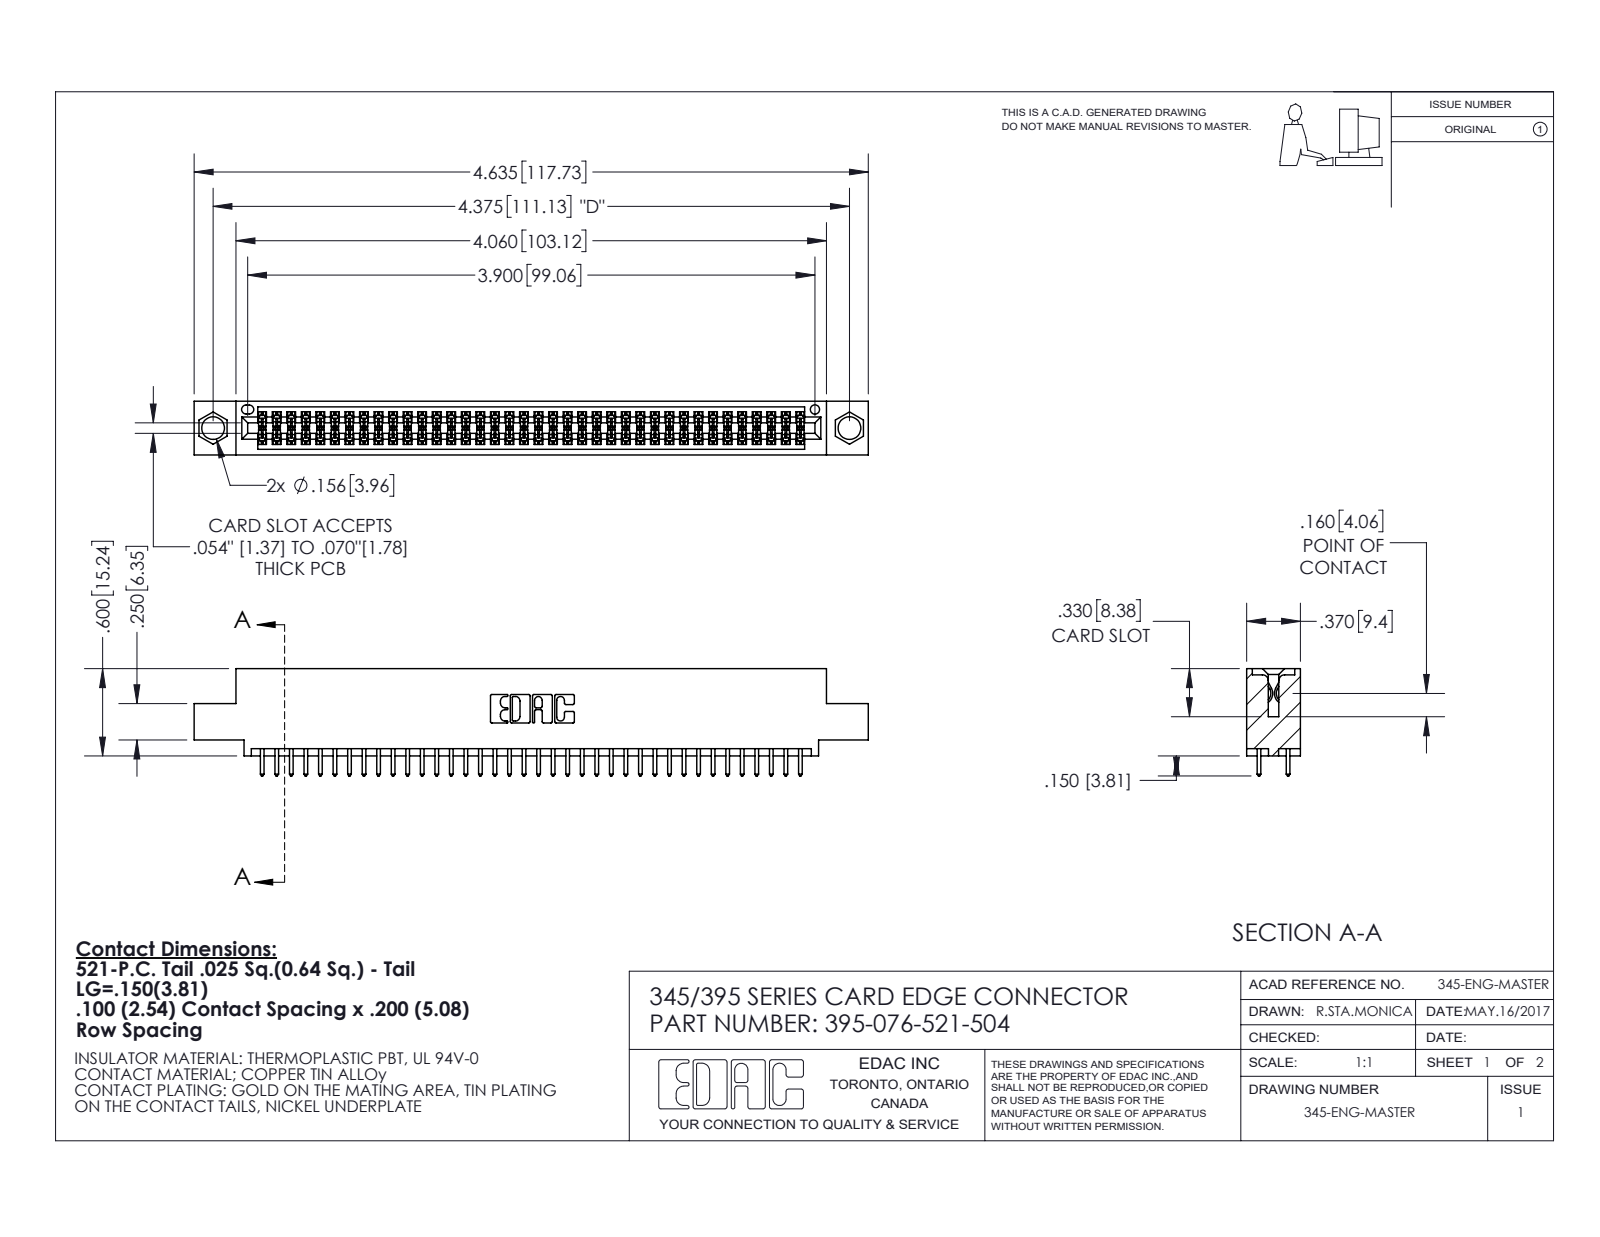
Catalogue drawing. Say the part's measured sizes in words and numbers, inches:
The part is named "345 Part_0.110 Offset - 0.156 Dia-TI; 395-076-521-504; 345-292-001_345-293-121". Its 3-D file was written by "SolidWorks 2020 (CONFIG_CONTROL_DESIGN)". It is 77 solids with 3944 faces: 2606 planar, 1338 cylindrical and 0 other. Overall it measures 4.635 by 0.737 by 0.37 inches. Its volume is 0.683 cubic inches and its surface area 25.12 square inches. Round holes: 2 of diameter 0.156, 1 of diameter 0.064. Partial cylindrical surfaces (rounded edges, fillets, slot ends): 152 of radius 0.006, 76 of radius 0.01, 22 of radius 0.01, 6 of radius 0.007, 6 of radius 0.031, 3 of radius 0.026, 2 of radius 0.014, 2 of radius 0.019. The main face-to-face distances are 0.072, 0.298, 0.2, 0.37, 0.098, 0.272, 0.025, 0.225, 0.175, 0.149. The hole center spacings are 0.27, 4.139, 4.375.
